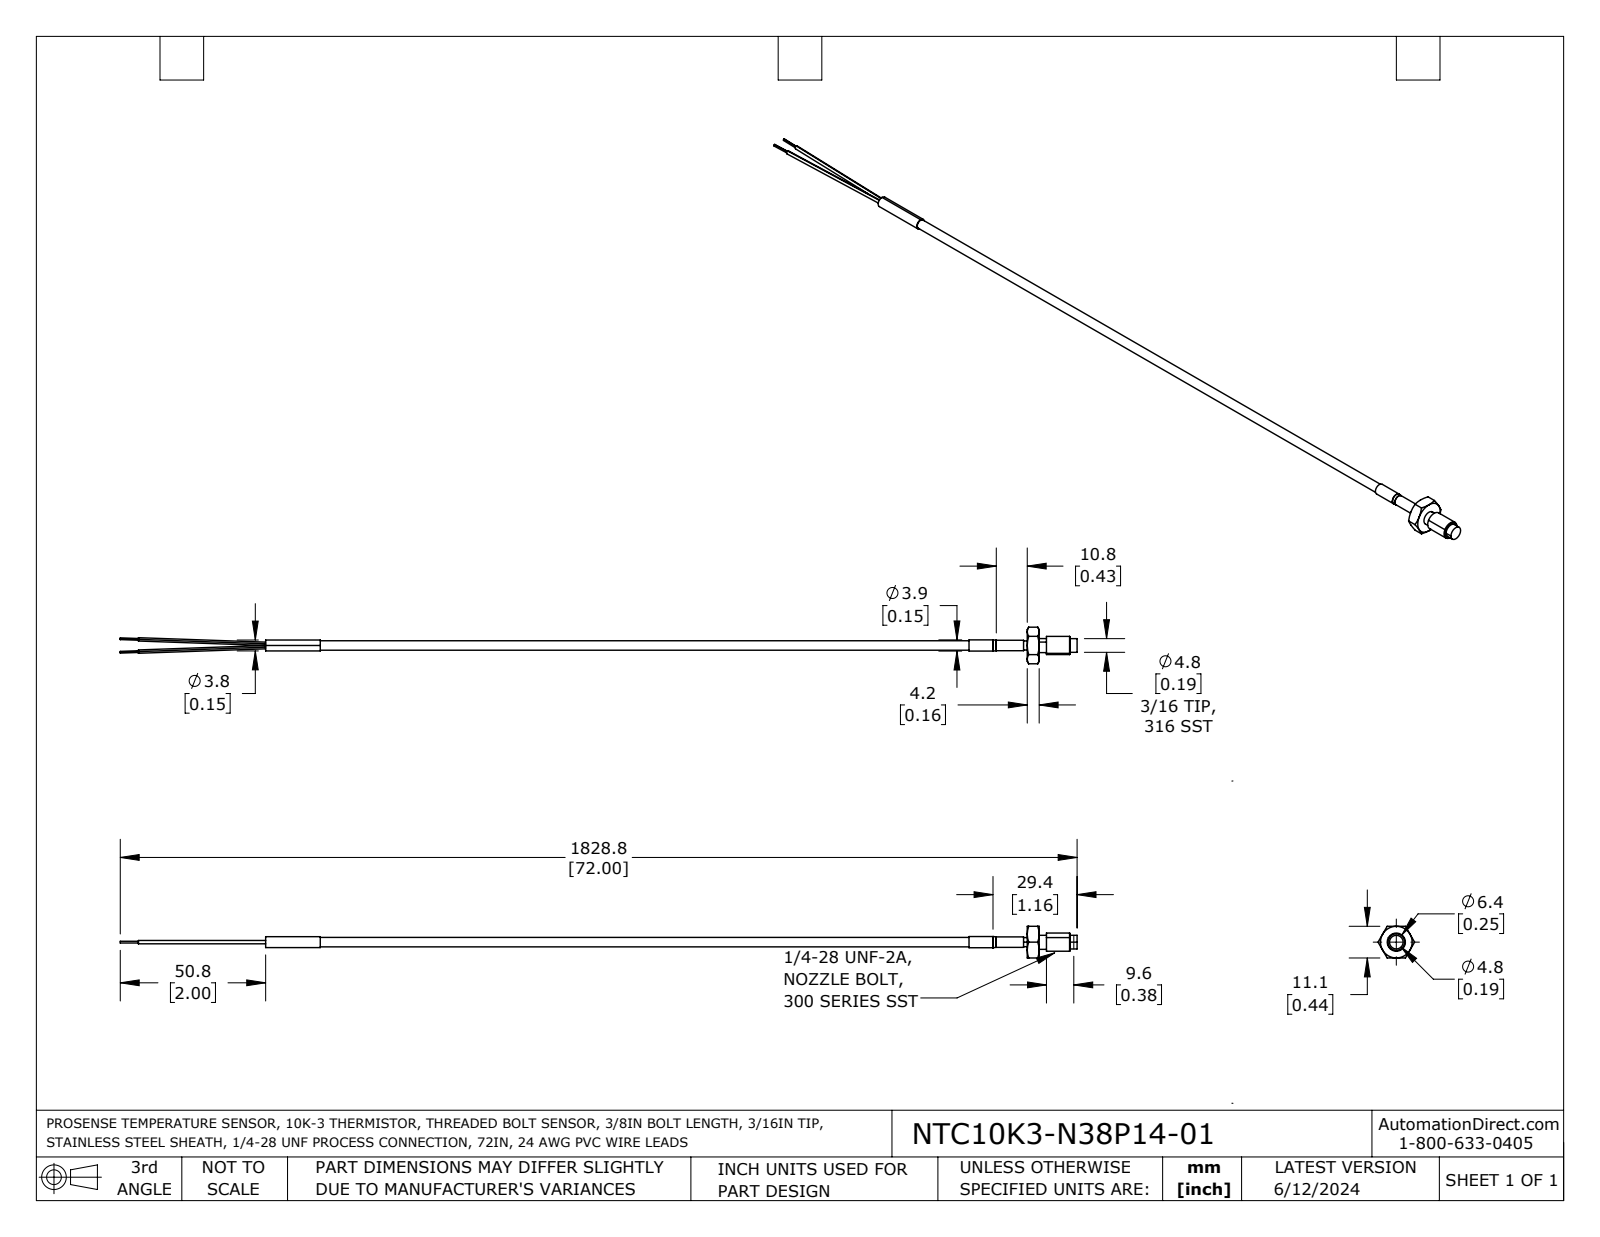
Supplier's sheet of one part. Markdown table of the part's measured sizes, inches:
| quantity | value |
| --- | --- |
| part name | NTC10K3-N38P14-01 |
| STEP written by | SolidWorks 2021 (AUTOMOTIVE_DESIGN) |
| units | inches |
| bodies | 3 solids, 94 faces (24 planar, 28 cylindrical, 42 other) |
| overall size | 13.156 × 0.503 × 0.436 |
| volume | 0.195 in³ |
| surface area | 7.602 in² |
| round holes (diameter × count) | 0.13 × 1, 0.131 × 1, 0.14 × 1 |
| round bosses / shafts (diameter × count) | 0.25 × 1, 0.193 × 1, 0.188 × 1, 0.154 × 1, 0.15 × 1, 0.144 × 1, 0.125 × 1 |
| main face-to-face distances | 0.164, 0.435, 0.471, 0.635, 0.1, 1.062, 0.591, 0.427, 0.735, 0.264 |
